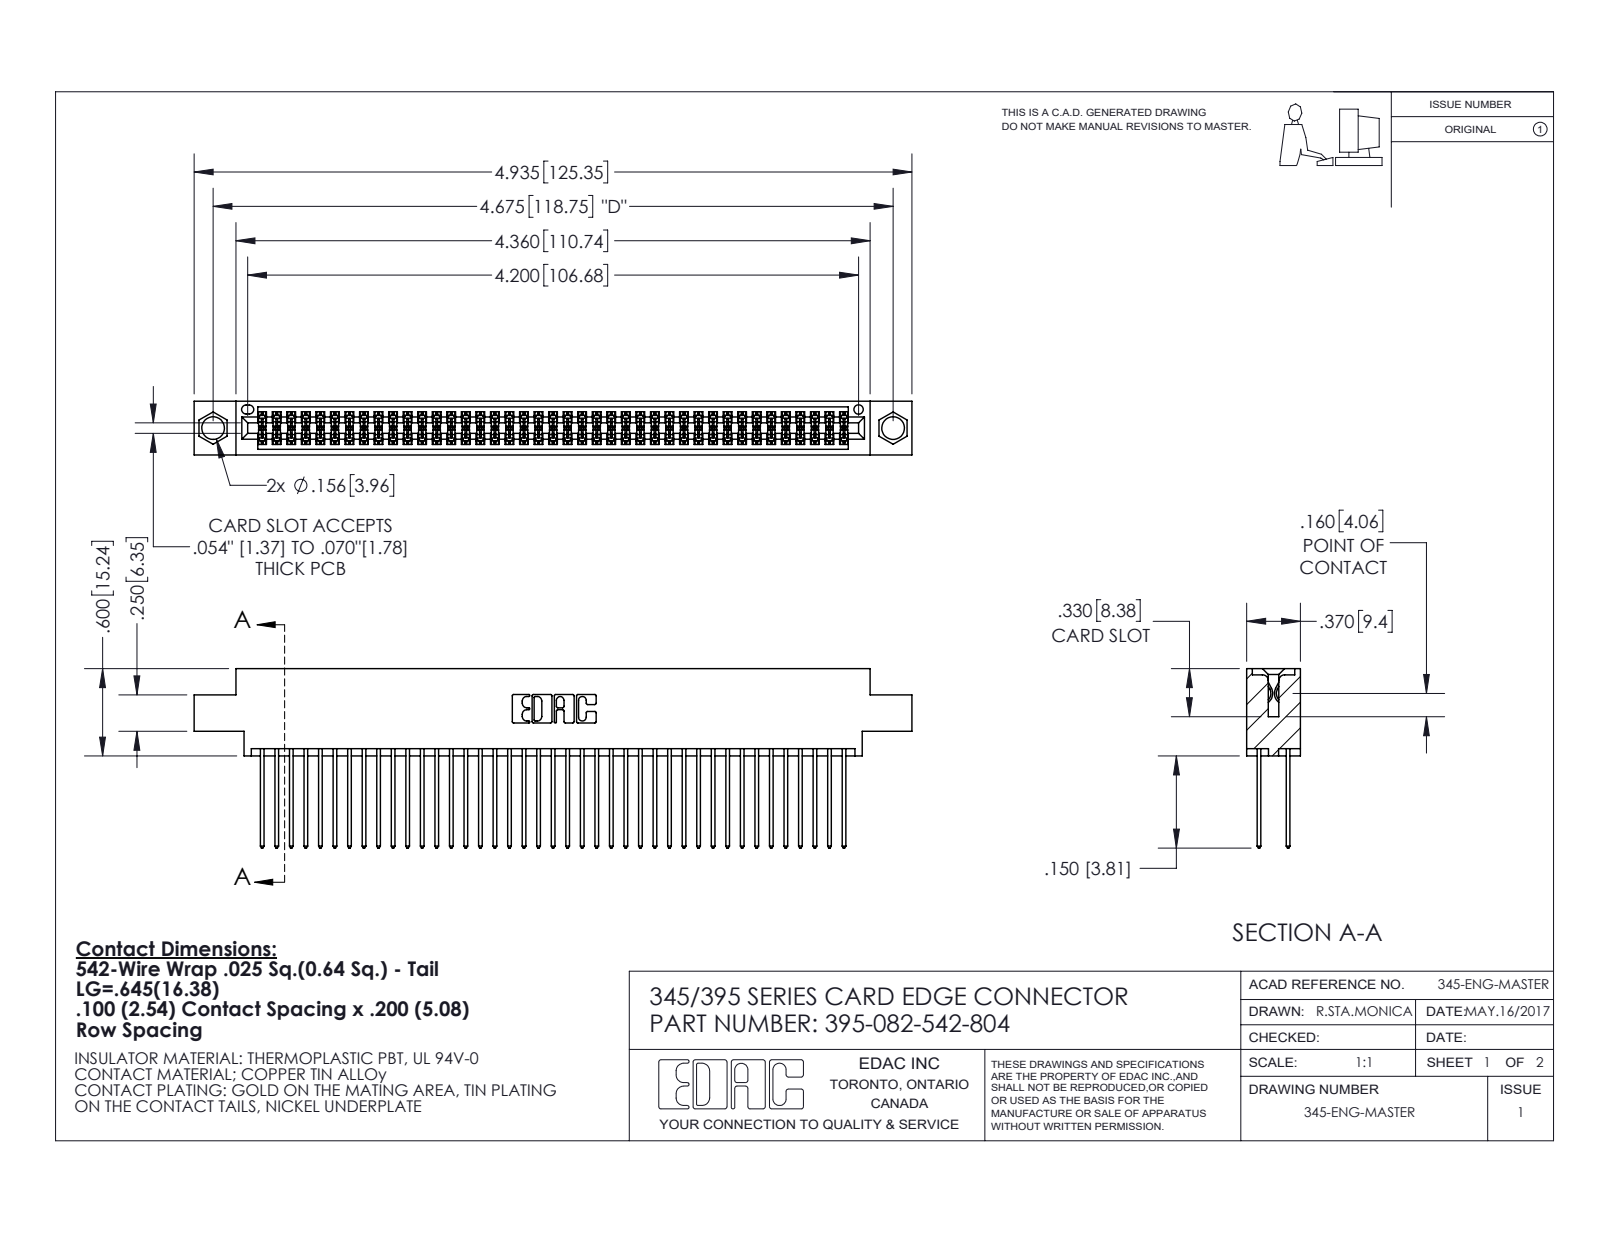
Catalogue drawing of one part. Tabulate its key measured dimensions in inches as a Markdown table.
| quantity | value |
| --- | --- |
| part name | 345 Part_0.170 Offset - 0.156 Dia-TI; 395-082-542-804; 345-292-001_345-293-142 |
| STEP written by | SolidWorks 2020 (CONFIG_CONTROL_DESIGN) |
| units | inches |
| bodies | 83 solids, 4244 faces (2804 planar, 1440 cylindrical, 0 other) |
| overall size | 4.935 × 1.232 × 0.37 |
| volume | 0.752 in³ |
| surface area | 30.98 in² |
| round holes (diameter × count) | 0.156 × 2, 0.064 × 1 |
| partial cylindrical surfaces (radius × count) | 0.006 × 123, 0.01 × 82, 0.01 × 22, 0.007 × 6, 0.031 × 6, 0.026 × 3, 0.014 × 2, 0.019 × 2 |
| main face-to-face distances | 0.072, 0.298, 0.2, 0.098, 0.272, 0.025, 0.37, 0.225, 0.175, 0.149 |
| hole center spacings | 0.27, 4.439, 4.675 |
